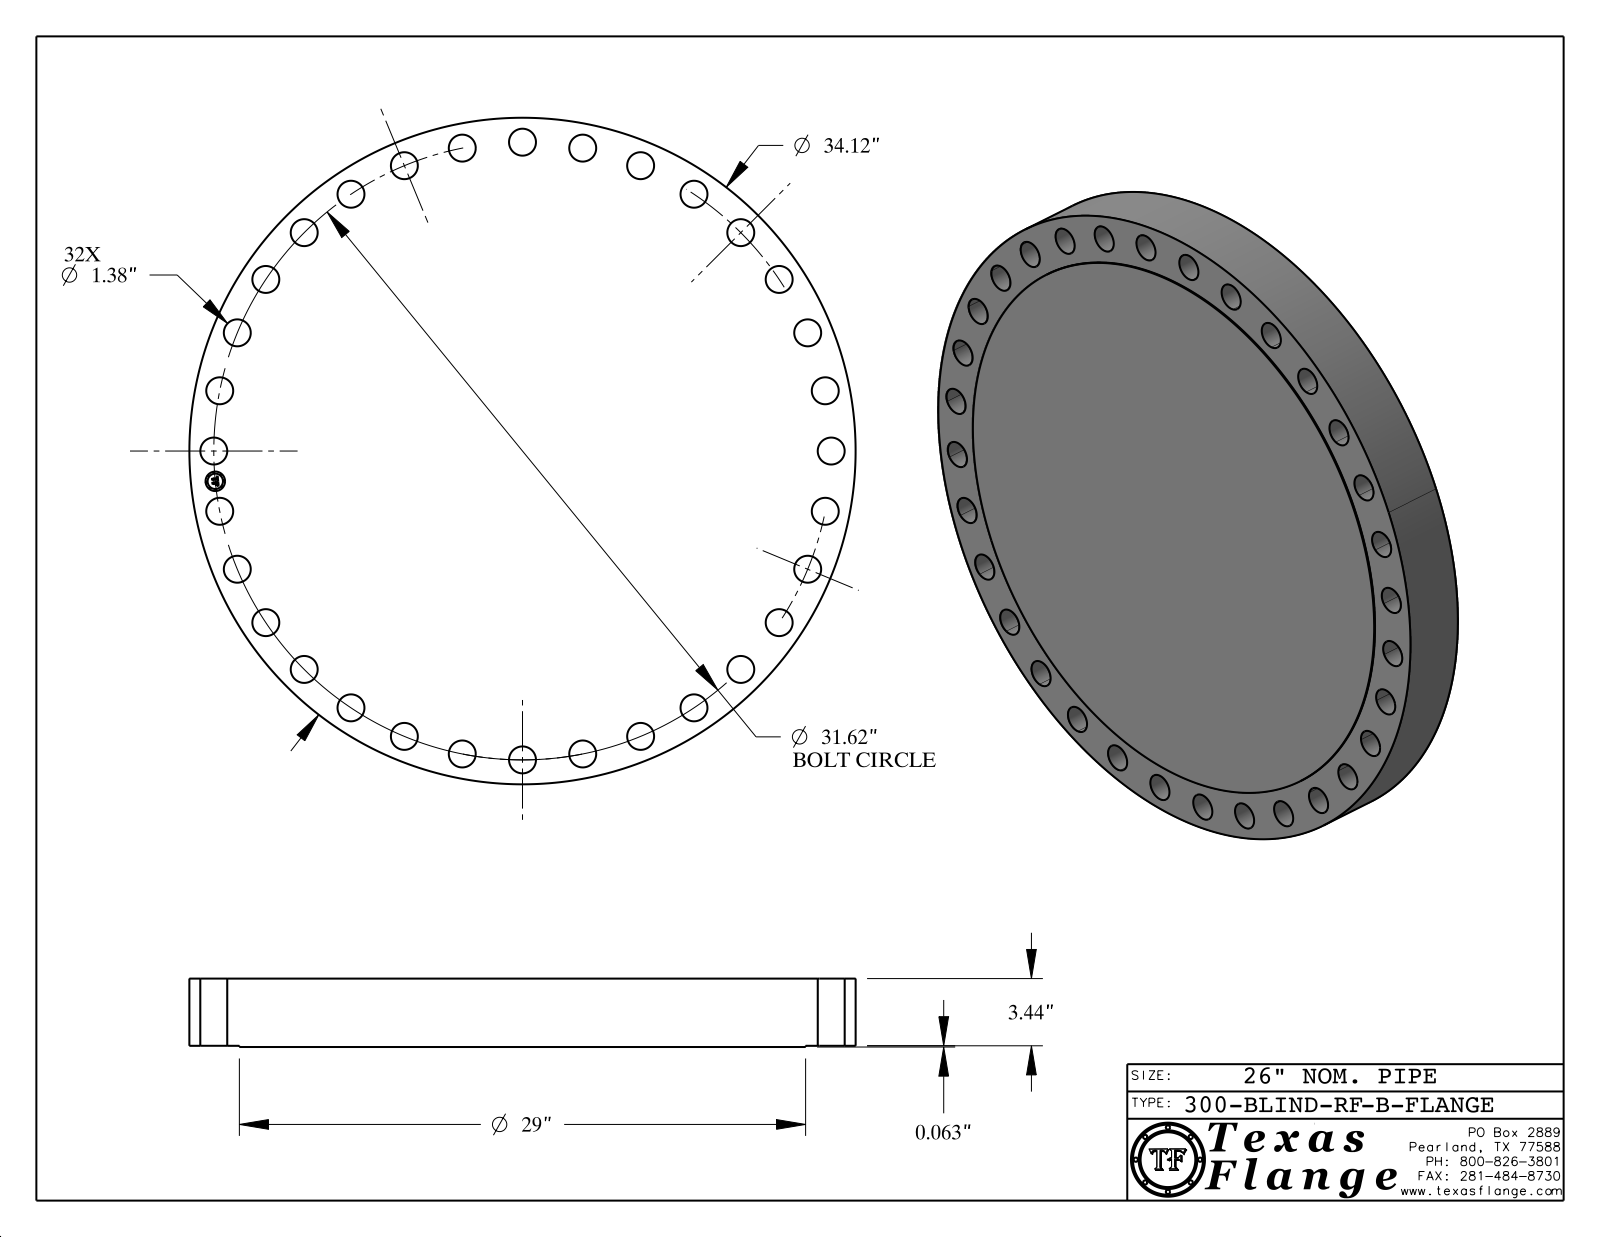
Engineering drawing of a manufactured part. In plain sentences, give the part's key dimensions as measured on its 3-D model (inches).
The part is named "300-BLIND-RF, Series B". Its 3-D file was written by "CATIA V5 STEP AP214 (AUTOMOTIVE_DESIGN)". It is 1 solid with 456 faces: 368 planar, 88 cylindrical and 0 other. Overall it measures 34.12 by 34.12 by 3.503 inches. Its volume is 3 022 cubic inches and its surface area 2 585 square inches. Round holes: 32 of diameter 1.38, 1 of diameter 1. Round bosses or shafts: 8 of diameter 0.061, 1 of diameter 34.12, 1 of diameter 29, 1 of diameter 0.788. The main face-to-face distances are 3.503, 0.063, 3.44, 3.488, 3.425, 0.015, 0.298, 0.293, 0.054, 0.193. The hole center spacings are 6.169, 26.291, 31.468, 27.887, 30.259, 14.906, 20.059, 31.013.
